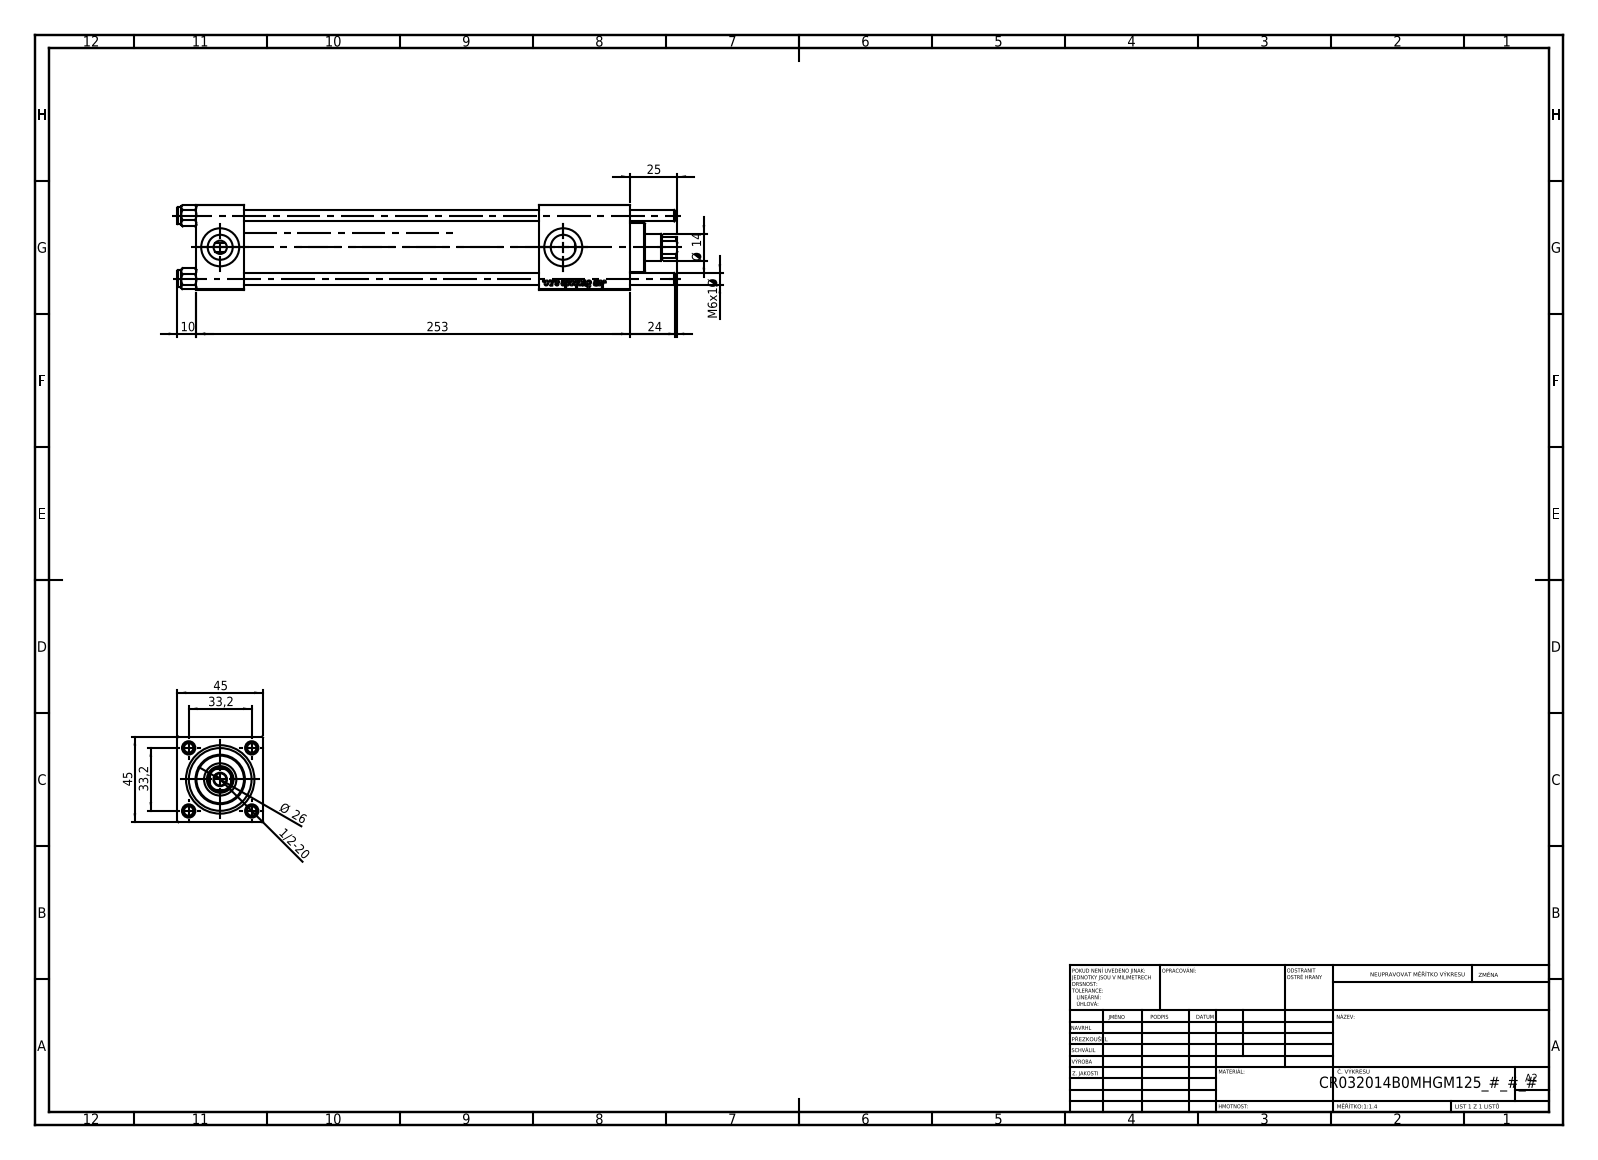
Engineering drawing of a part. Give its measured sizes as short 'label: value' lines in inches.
name: V215CR_B_TYCINKA; V215CR_VCP_B; V215_VC_A; NUT_M5_B (+1 more)
written by: SolidWorks 2019 (CONFIG_CONTROL_DESIGN)
unit: in
bodies: 11 solids, 1157 faces (431 planar, 78 cylindrical, 648 other)
size: 10.354 × 1.772 × 1.772
volume: 15.93 in³; area: 167.7 in²
holes: 4× ⌀0.236, 2× ⌀0.276, 2× ⌀0.518, 2× ⌀0.787, 1× ⌀0.256, 1× ⌀0.551, 1× ⌀0.669, 1× ⌀0.945, 1× ⌀1.26, 1× ⌀1.299
bosses: 4× ⌀0.354, 1× ⌀1.496, 1× ⌀1.024
rounds: 1× R0.256
face distances: 1.772, 0.984, 8.976, 7.992, 7.087, 6.102, 1.89, 7.846, 6.862, 0.76
hole spacings: 0.924, 1.307, 1.848, 7.106
